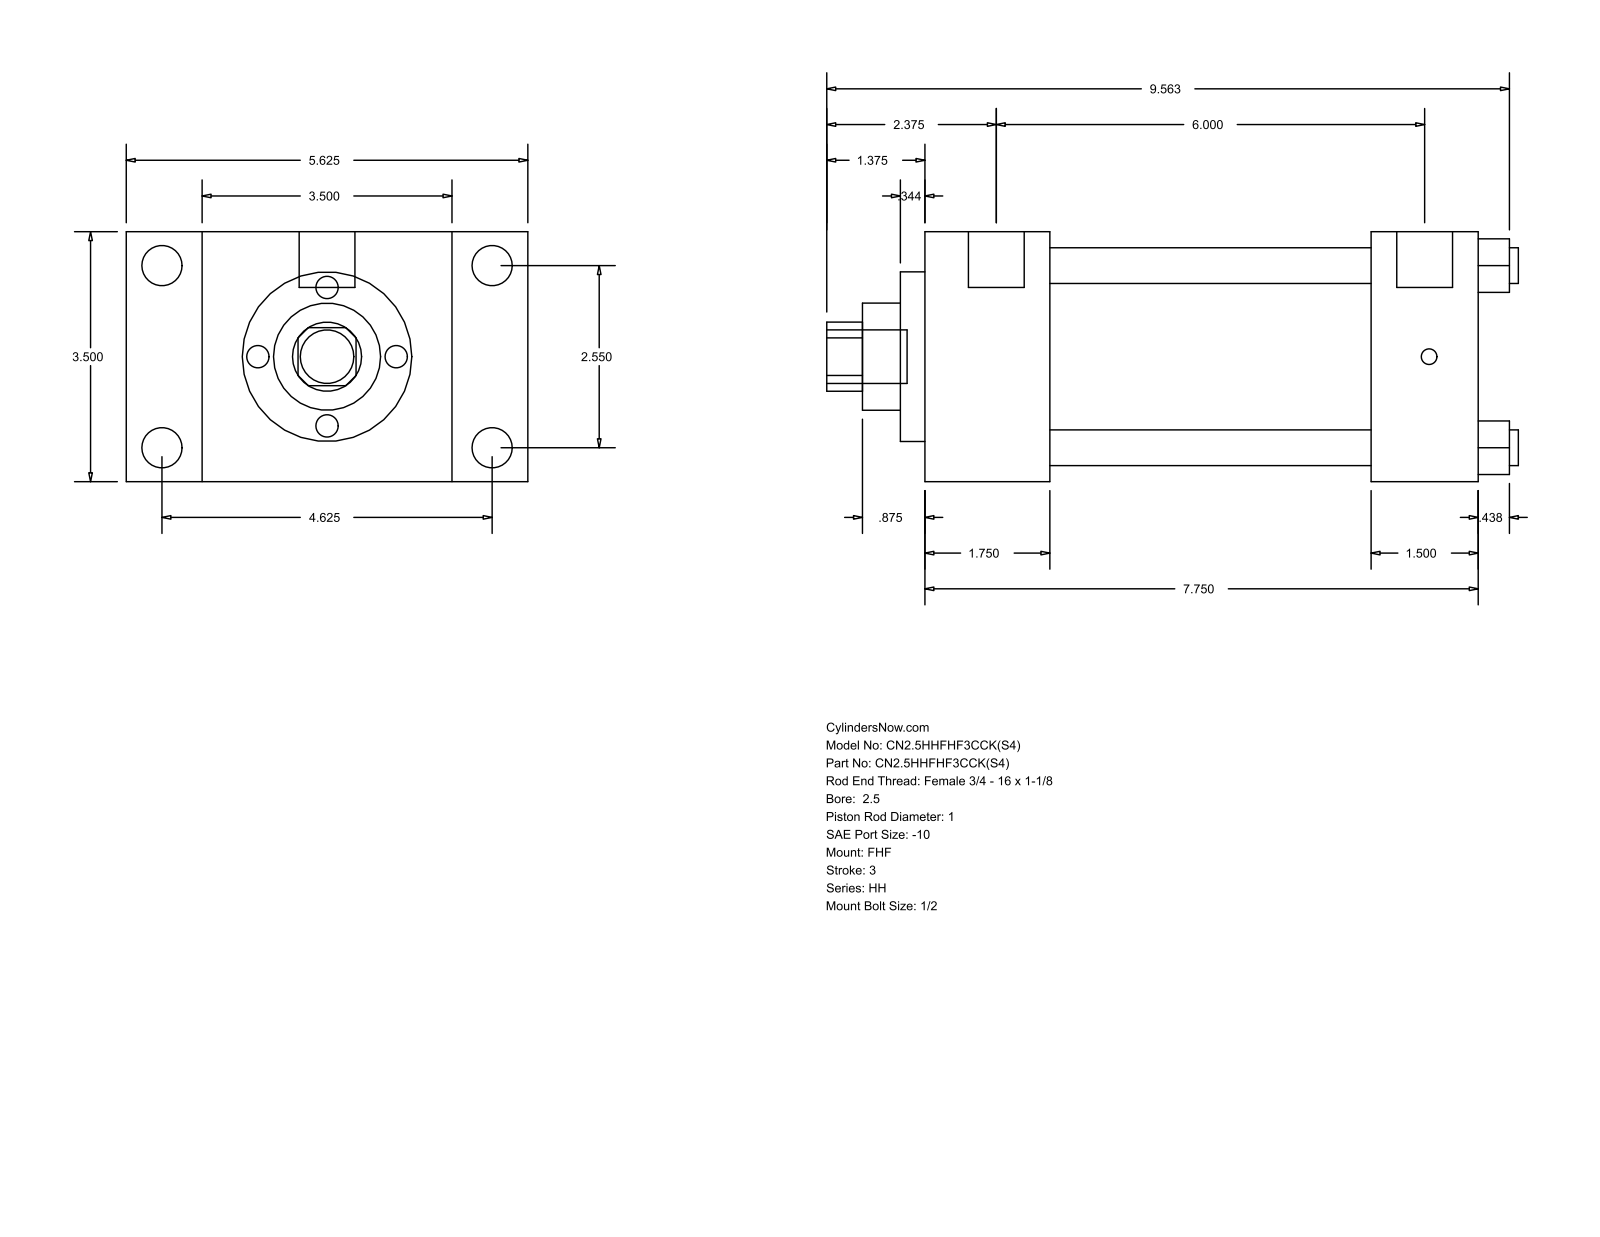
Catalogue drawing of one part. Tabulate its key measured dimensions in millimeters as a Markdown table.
| quantity | value |
| --- | --- |
| part name | HH_FHF__0250_1 |
| STEP written by | GSSL Pune (CONFIG_CONTROL_DESIGN) |
| units | millimeters |
| bodies | 0 solids, 90 faces (61 planar, 29 cylindrical, 0 other) |
| overall size | 246.06 × 142.88 × 88.9 |
| round holes (diameter × count) | 12.7 × 4, 25.4 × 1, 38.1 × 1, 60.33 × 1, 73.03 × 1 |
| round bosses / shafts (diameter × count) | 14.3 × 4, 5.56 × 4, 19.84 × 2, 19.05 × 1 |
| partial cylindrical surfaces (radius × count) | 12.29 × 1 |
| main face-to-face distances | 88.9, 44.46, 26.99, 115.89, 196.86, 152.4, 142.88, 158.76, 114.3, 38.1 |
| hole center spacings | 45.79, 64.76, 91.58 |
